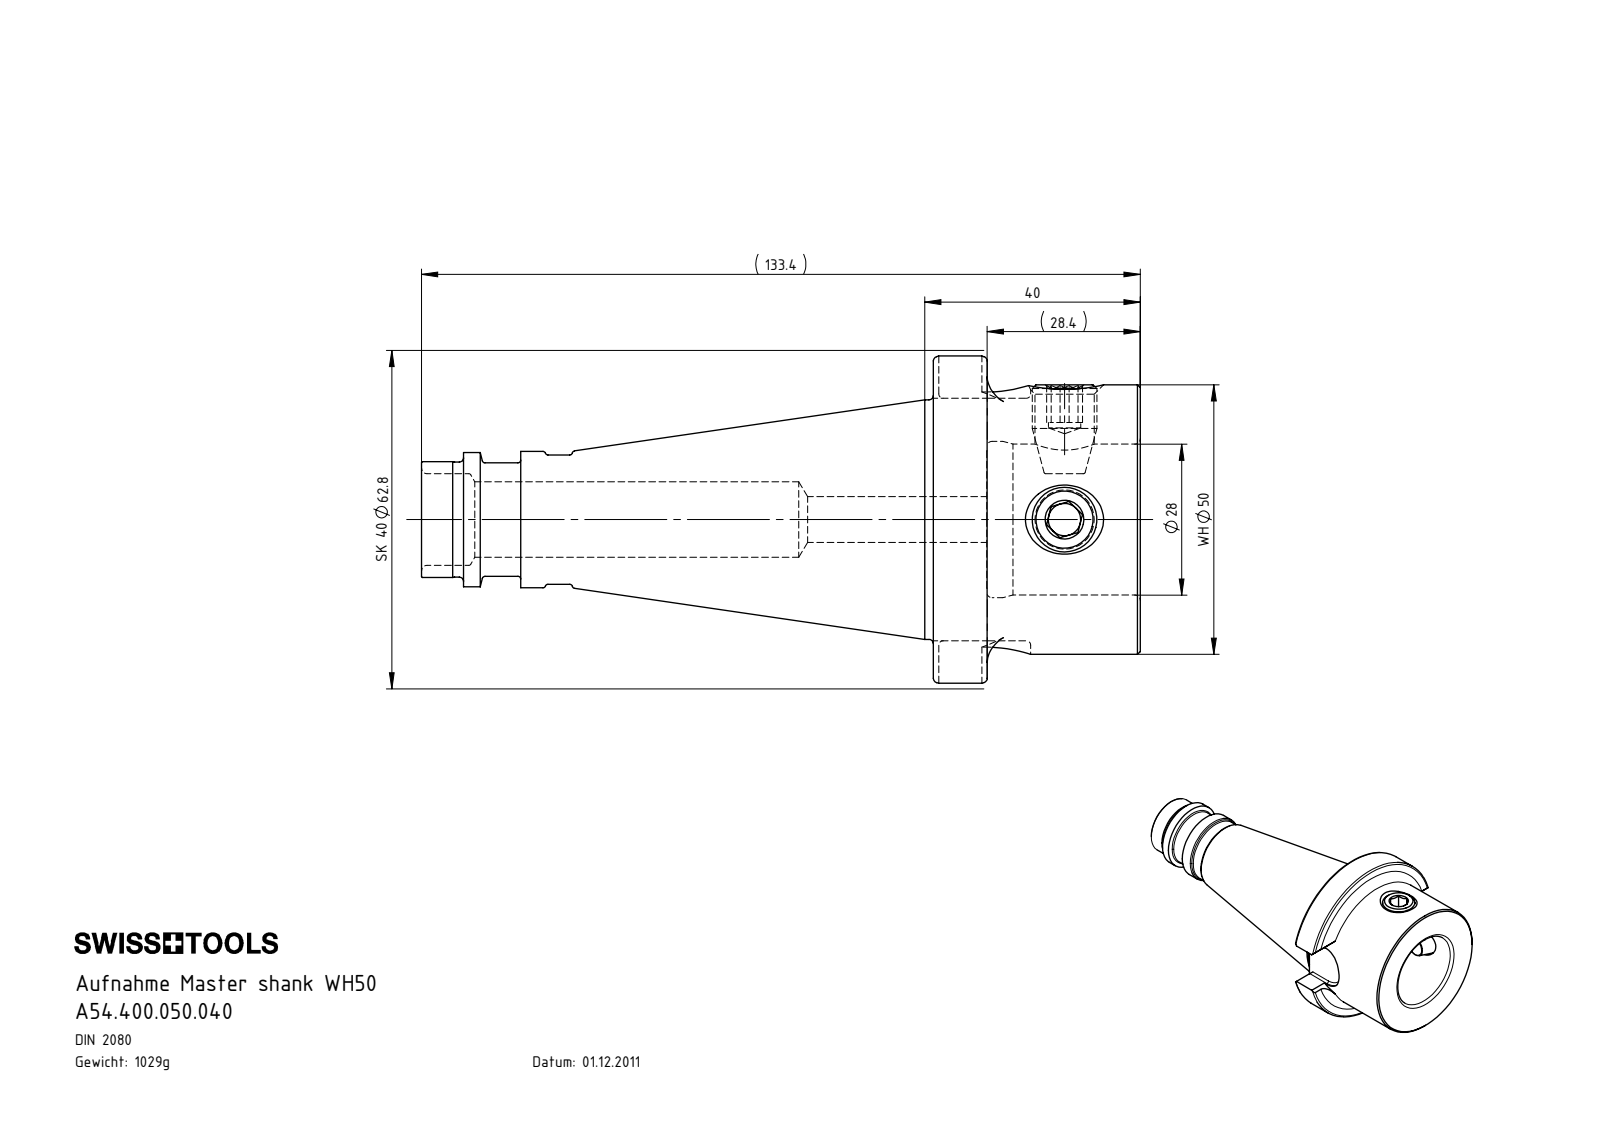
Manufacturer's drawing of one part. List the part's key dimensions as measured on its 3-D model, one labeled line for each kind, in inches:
Part name (STEP PRODUCT): SZ4-WH5.K01.040_B; A54.400.050.040; WH5-ER1.001.017
STEP written by: SolidWorks 2022 (CONFIG_CONTROL_DESIGN)
Units: inches
Bodies: 3 solids, 178 faces (54 planar, 49 cylindrical, 75 other)
Overall size (bounding box): 5.252 × 2.472 × 2.39
Volume: 8 in³ · Surface area: 45.47 in²
Round holes (diameter × count): ⌀0.236 ×2, ⌀0.433 ×2, ⌀0.335 ×1, ⌀0.551 ×1, ⌀0.669 ×1, ⌀1.004 ×1, ⌀1.102 ×1, ⌀1.142 ×1
Round bosses / shafts (diameter × count): ⌀0.472 ×2, ⌀2.472 ×1, ⌀1.969 ×1, ⌀1.75 ×1, ⌀0.996 ×1, ⌀0.981 ×1, ⌀0.945 ×1, ⌀0.846 ×1
Partial cylindrical surfaces — rounded edges, fillets, slot ends (radius × count): R0.031 ×4, R0.317 ×1
Main face-to-face distances: 1.512, 0.394, 1.118, 0.39, 1.122, 1.772, 3.016, 3.406, 3.409, 4.528
